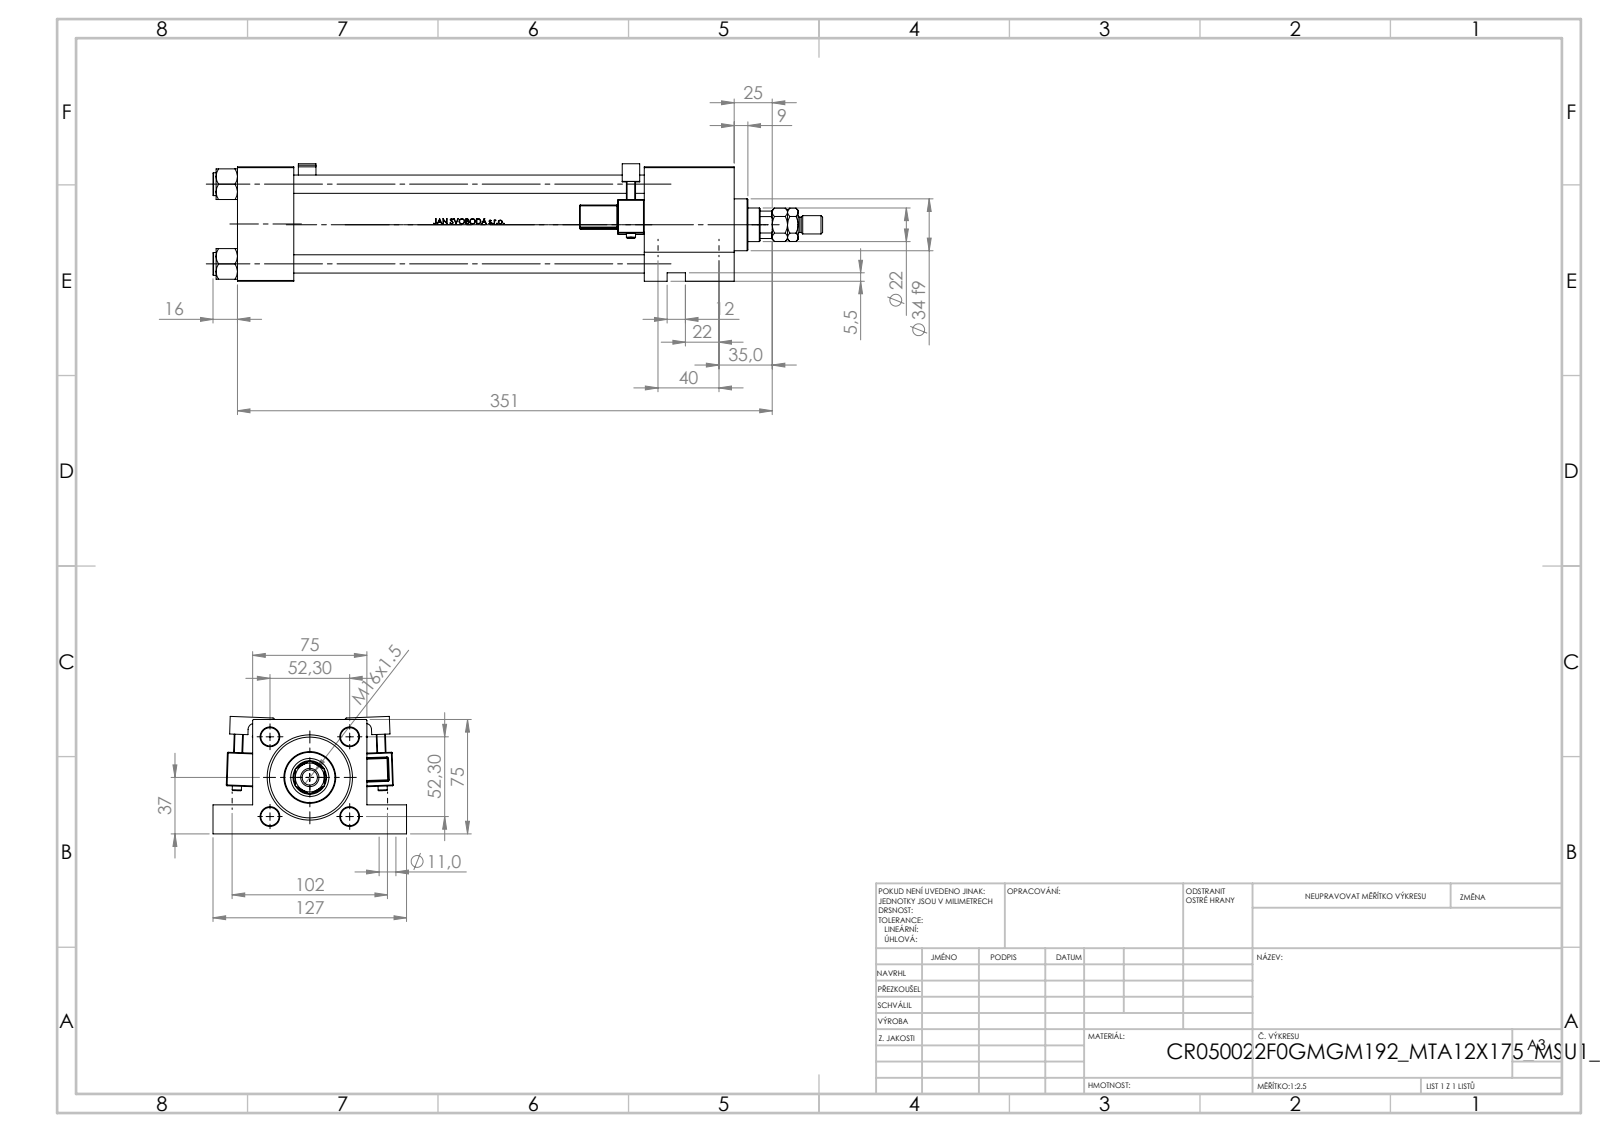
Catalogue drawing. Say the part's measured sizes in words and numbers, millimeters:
The part is named "MTA; V215_VC_A; V215CR_F_TYCINKA; V215CR_MSU (+3 more)". Its 3-D file was written by "SolidWorks 2019 (CONFIG_CONTROL_DESIGN)". It is 14 solids with 1306 faces: 510 planar, 190 cylindrical and 606 other. Overall it measures 400 by 127 by 77.03 millimeters. Its volume is 983 933 cubic millimeters and its surface area 266 040 square millimeters. Round holes: 4 of diameter 11, 4 of diameter 12, 2 of diameter 7, 2 of diameter 30, 1 of diameter 10.5, 1 of diameter 17, 1 of diameter 20.96, 1 of diameter 22, 1 of diameter 25, 1 of diameter 41, 1 of diameter 50, 1 of diameter 53. Round bosses or shafts: 4 of diameter 15, 2 of diameter 6, 1 of diameter 56, 1 of diameter 34, 1 of diameter 12, 1 of diameter 10. Partial cylindrical surfaces (rounded edges, fillets, slot ends): 48 of radius 0.5, 2 of radius 1, 2 of radius 2.5, 2 of radius 4, 1 of radius 10.5. The main face-to-face distances are 75, 37, 326, 289, 267, 230, 59, 19, 56, 297.3. The hole center spacings are 52.3, 36.63, 37.34, 40, 73.96, 102, 109.56, 265.5.
